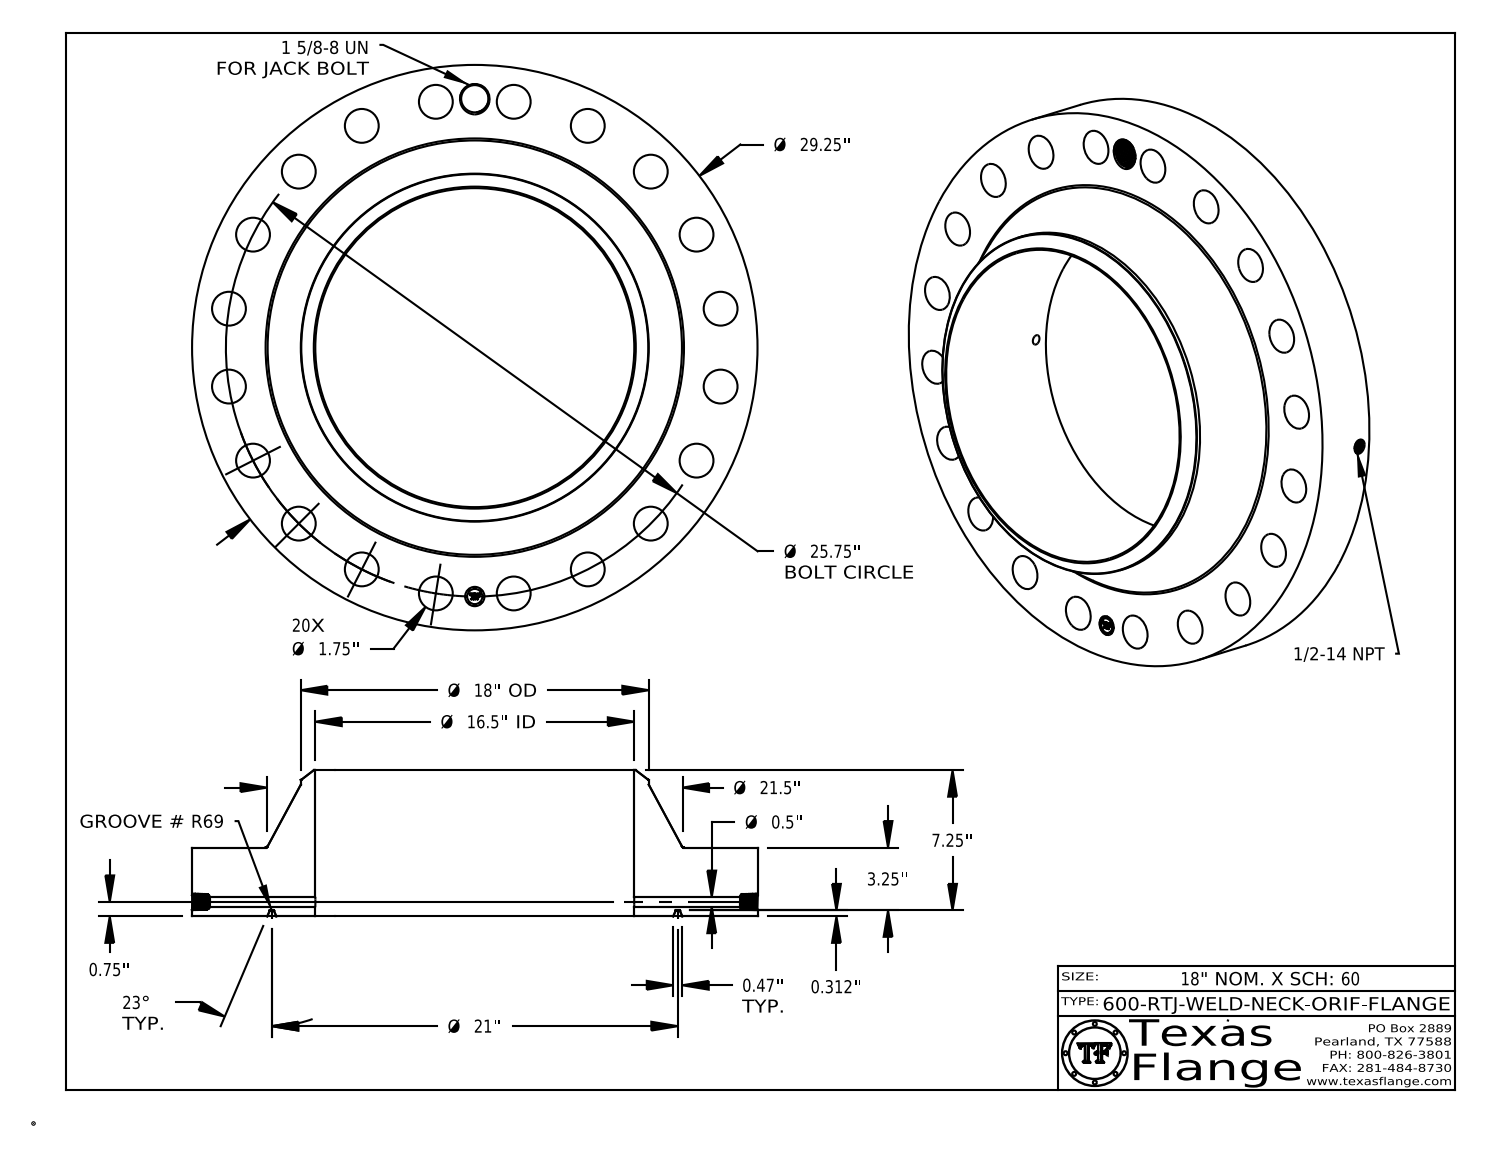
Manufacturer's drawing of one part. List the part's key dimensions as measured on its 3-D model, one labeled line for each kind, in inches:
Part name (STEP PRODUCT): 600-RTJ-WELD-NECK
STEP written by: CATIA V5 STEP AP214 (AUTOMOTIVE_DESIGN)
Units: inches
Bodies: 1 solid, 883 faces (370 planar, 142 cylindrical, 371 other)
Overall size (bounding box): 29.25 × 29.25 × 7.562
Volume: 1 769 in³ · Surface area: 2 154 in²
Round holes (diameter × count): ⌀1.75 ×20, ⌀0.5 ×1, ⌀0.672 ×1, ⌀1 ×1, ⌀1.409 ×1, ⌀16.5 ×1
Round bosses / shafts (diameter × count): ⌀0.061 ×8, ⌀29.25 ×1, ⌀18 ×1, ⌀0.788 ×1
Main face-to-face distances: 3.562, 0.312, 3.25, 7.562, 7.25, 4, 0.015, 3.547, 3.235, 4.015
Hole centre spacings: 15.135, 24.49, 25.433, 12.875, 11.69, 4.028, 7.957, 18.208
